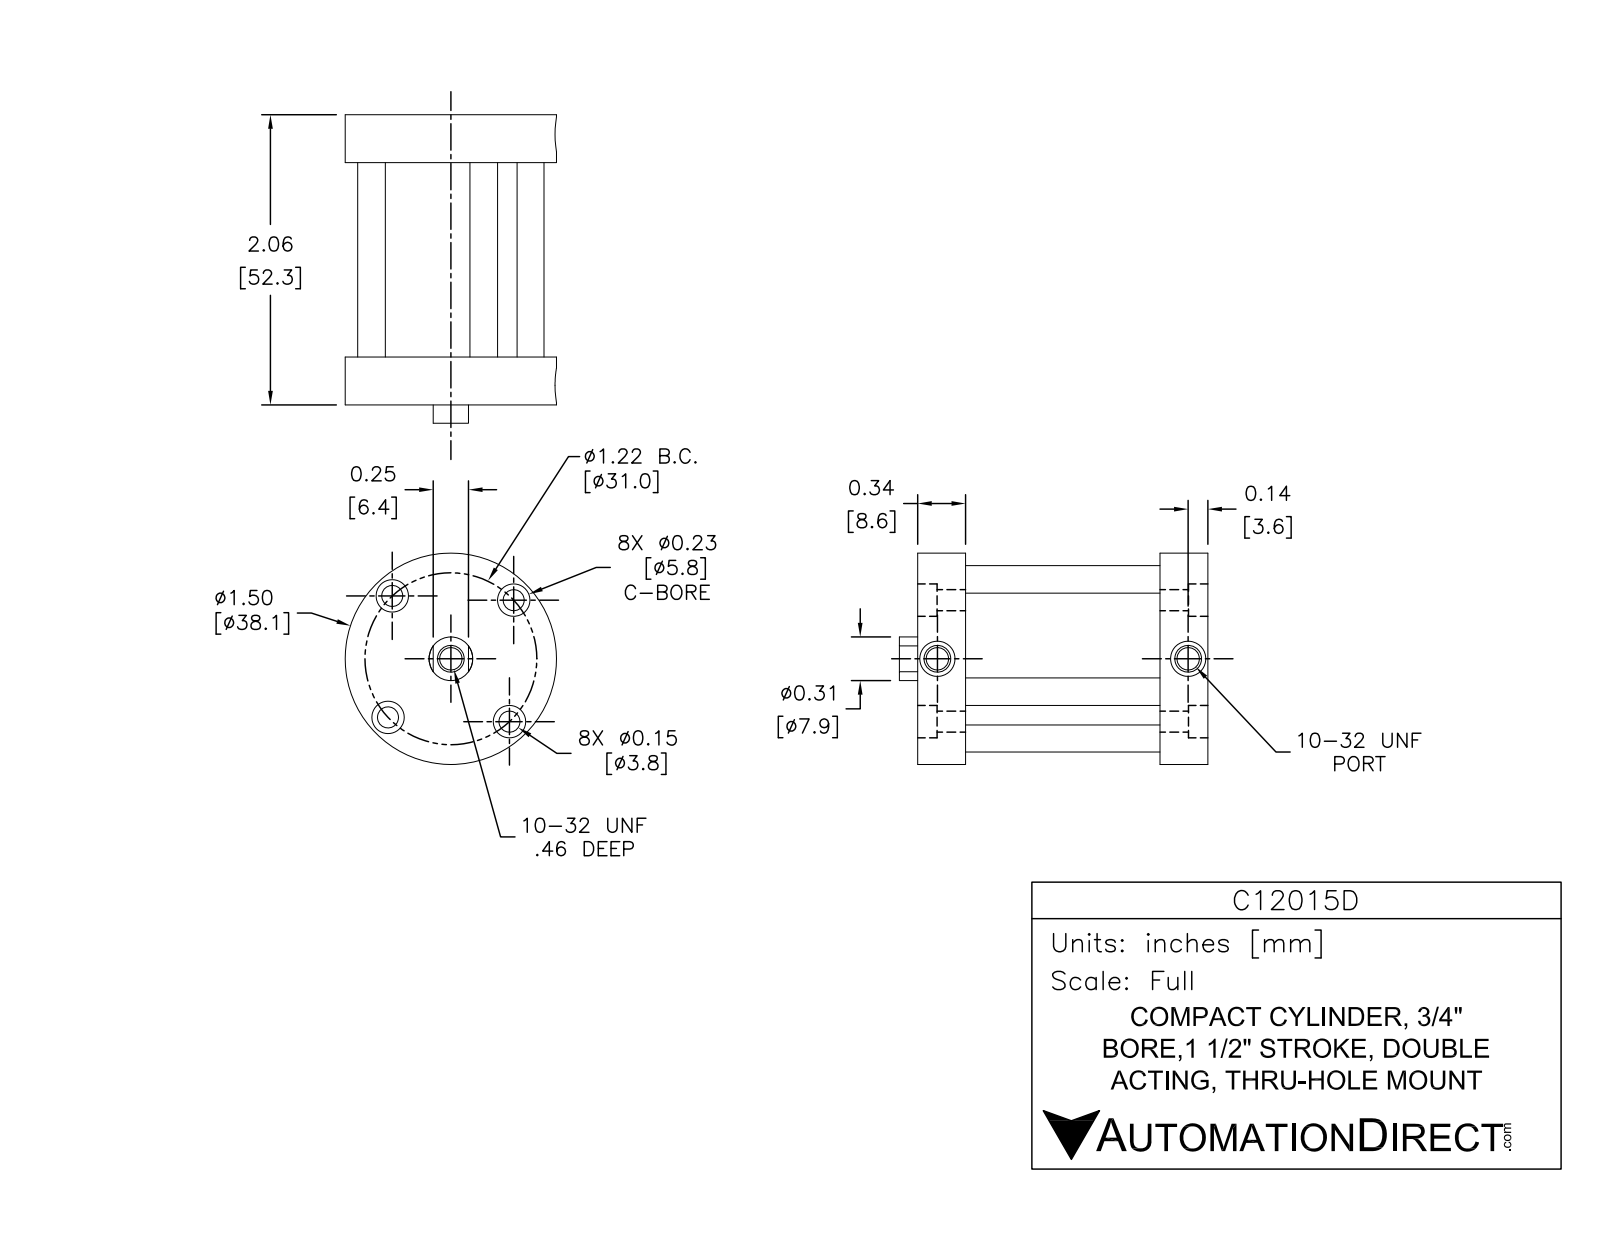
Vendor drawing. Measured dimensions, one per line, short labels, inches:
name: C12015D; C12015D-FO1_BM_r; C12015D-rod_part; C12015D-FO1_BM_rod (+3 more)
written by: SolidWorks 2014 (AUTOMOTIVE_DESIGN)
unit: in
bodies: 9 solids, 165 faces (51 planar, 104 cylindrical, 10 other)
size: 2.19 × 1.5 × 1.5
volume: 1.588 in³; area: 31.55 in²
holes: 4× ⌀0.136, 4× ⌀0.156, 4× ⌀0.235, 3× ⌀0.156, 2× ⌀0.313, 1× ⌀0.31, 1× ⌀0.312, 1× ⌀0.75, 1× ⌀0.812
bosses: 4× ⌀0.272, 1× ⌀1.5
face distances: 0.17, 1.72, 1.55, 2.06, 0.34, 0.34, 1.38, 1.72, 1.89, 1.89
hole spacings: 0.61, 0.863, 0.331, 0.596, 1.065, 1.174, 1.22, 1.78
